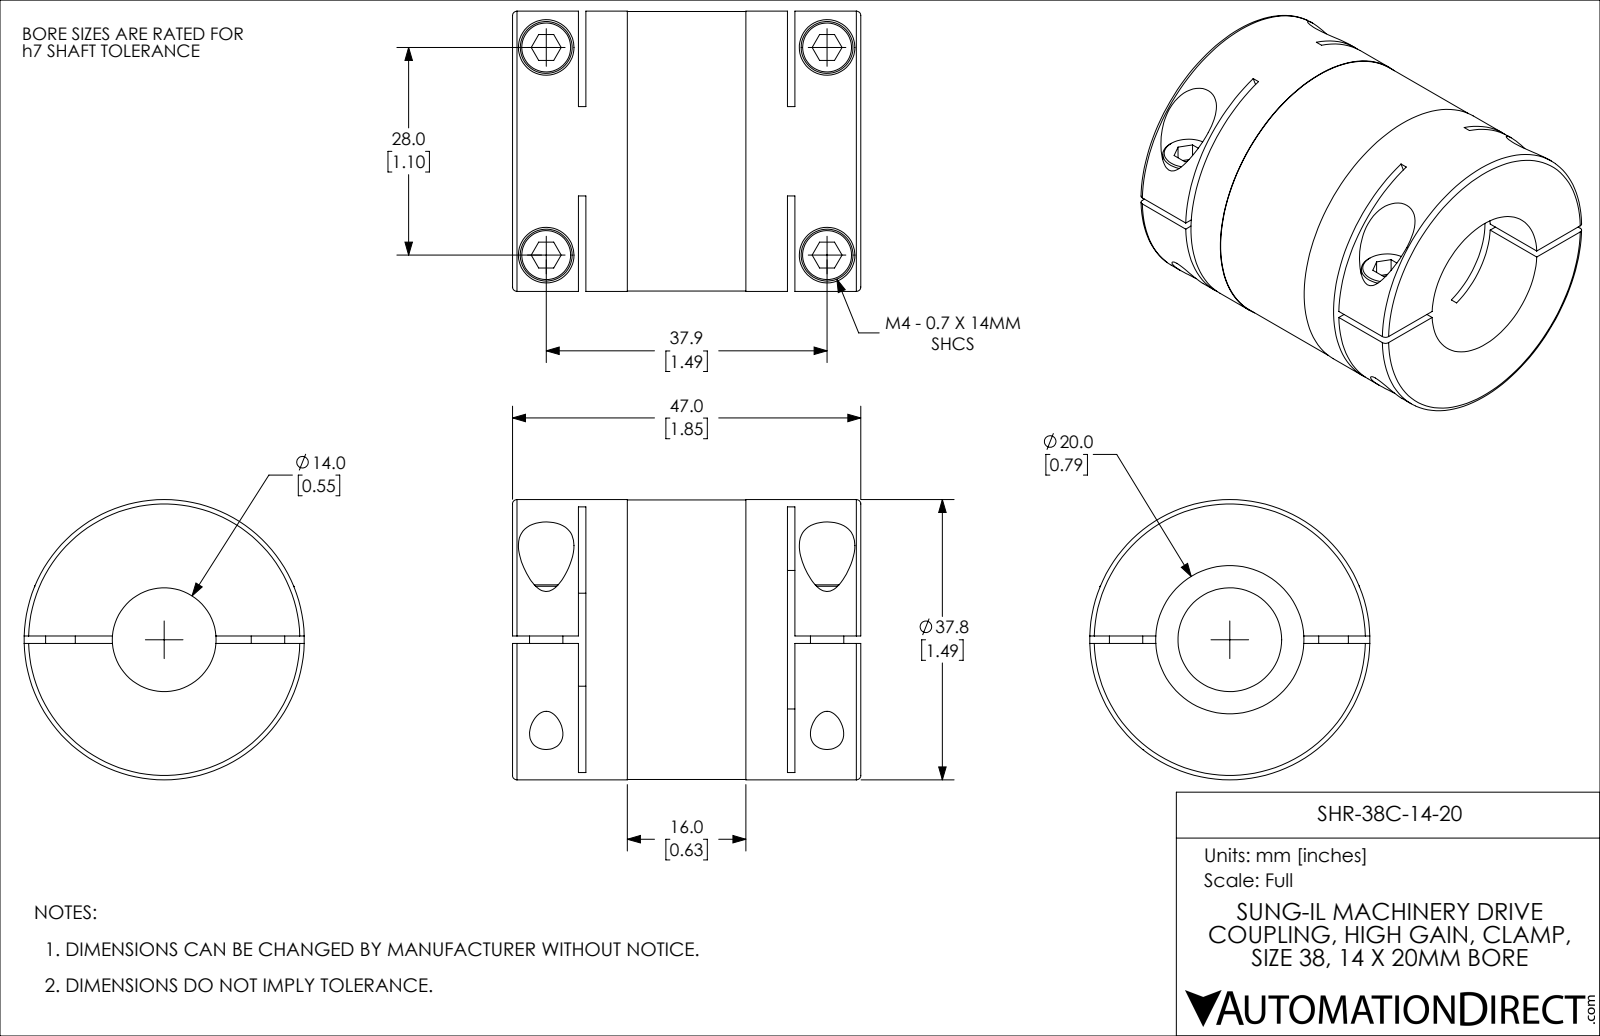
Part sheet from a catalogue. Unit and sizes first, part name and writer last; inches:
Units: inches
Overall size (bounding box): 1.85 × 1.488 × 1.488
Round holes (diameter × count): ⌀0.177 ×4, ⌀0.295 ×4, ⌀0.551 ×1, ⌀0.787 ×1, ⌀0.866 ×1
Round bosses / shafts (diameter × count): ⌀0.276 ×4, ⌀0.157 ×2, ⌀1.488 ×1, ⌀1.484 ×1
Partial cylindrical surfaces — rounded edges, fillets, slot ends (radius × count): R1.969 ×2
Main face-to-face distances: 0.039, 0.39, 1.461, 0.35, 1.5, 1.11, 1.85, 1.071, 1.15, 1.24
Hole centre spacings: 1.102, 1.492, 1.855
Volume: 2.212 in³ · Surface area: 23.88 in²
Bodies: 1 solid, 144 faces (70 planar, 58 cylindrical, 16 other)
Part name (STEP PRODUCT): SHR-38C-14-20
STEP written by: SolidWorks 2021 (CONFIG_CONTROL_DESIGN)
